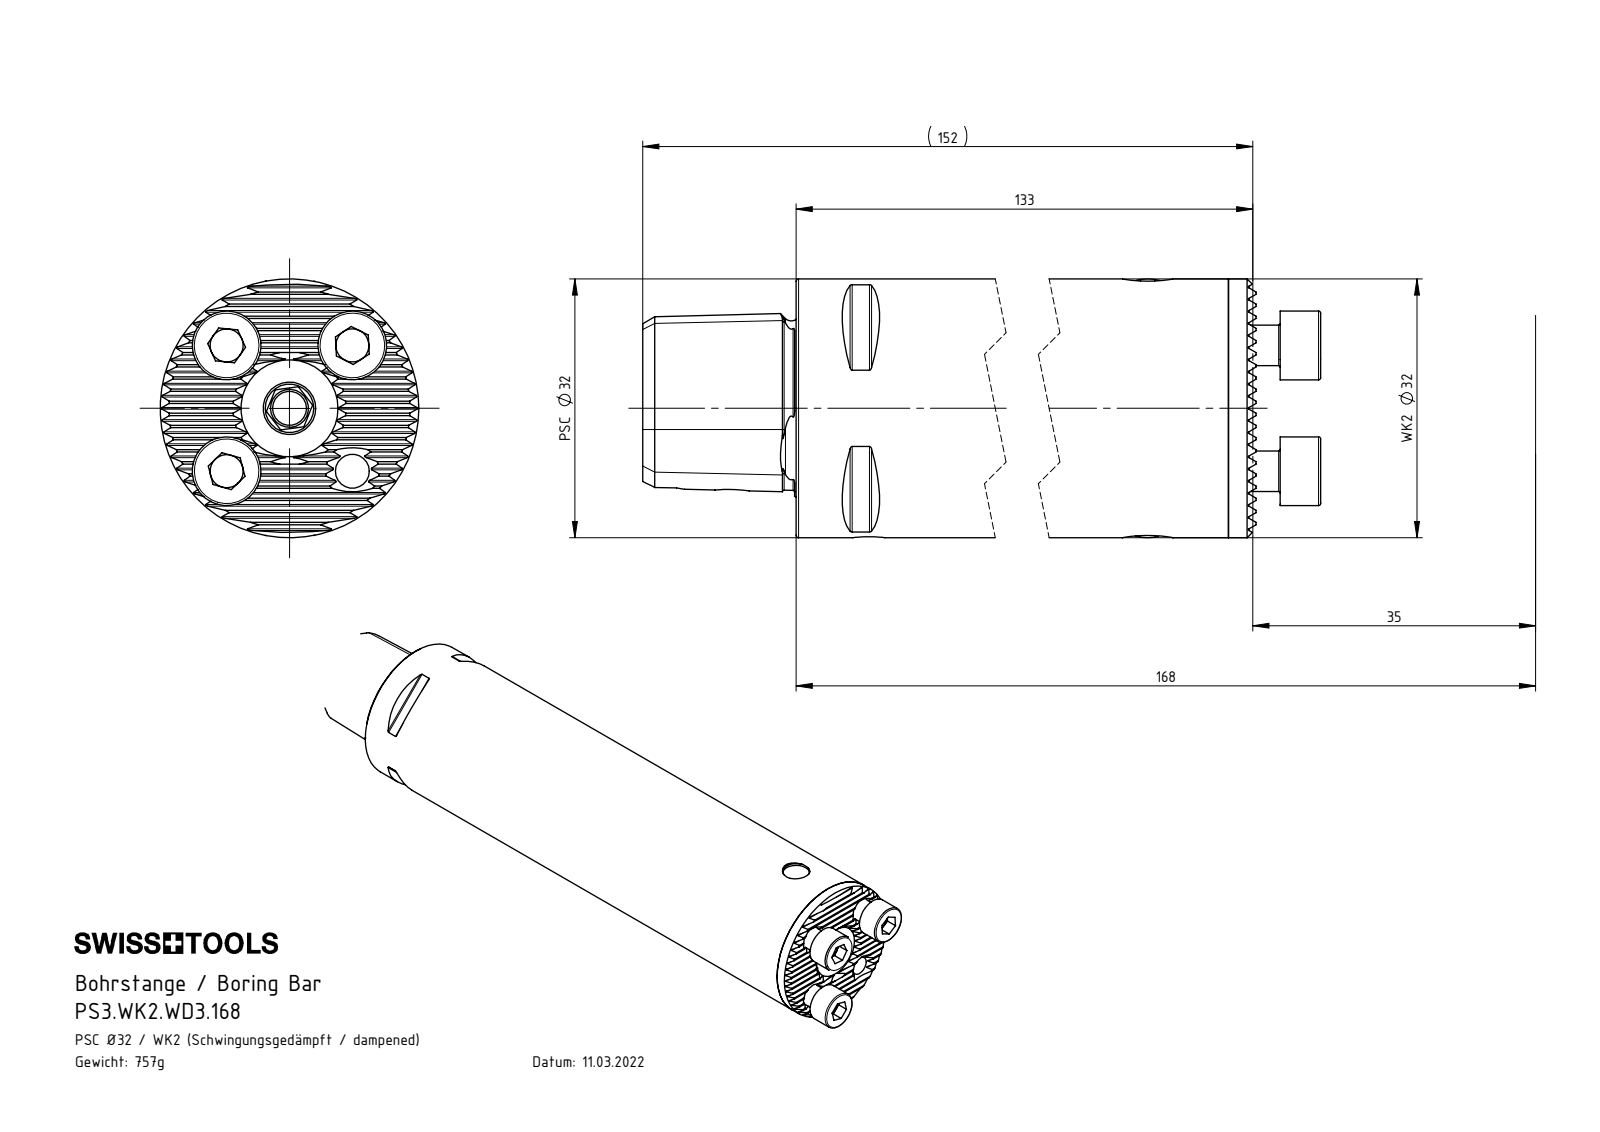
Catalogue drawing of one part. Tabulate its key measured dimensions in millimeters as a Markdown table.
| quantity | value |
| --- | --- |
| part name | DIN 3771 - 23x2; WD3-WK2.032.003_A; DIN 3771 - 6x1; WD3-ER1.027.019_A (+8 more) |
| STEP written by | SolidWorks 2017 (AUTOMOTIVE_DESIGN) |
| units | millimeters |
| bodies | 16 solids, 673 faces (236 planar, 163 cylindrical, 274 other) |
| overall size | 160.4 × 32 × 32 |
| volume | 100 978 mm³ |
| surface area | 56 780 mm² |
| round holes (diameter × count) | 4.2 × 5, 6 × 2, 3.6 × 1, 4 × 1, 6.8 × 1, 7 × 1, 7.4 × 1, 8.2 × 1, 8.5 × 1, 10.2 × 1, 12 × 1, 14 × 1 |
| round bosses / shafts (diameter × count) | 8.5 × 3, 5 × 3, 32 × 1, 27 × 1, 26.7 × 1, 26 × 1, 23.8 × 1, 13 × 1 |
| partial cylindrical surfaces (radius × count) | 0.12 × 21, 0.3 × 8, 3 × 1 |
| main face-to-face distances | 6, 93.4, 2.6, 1.3, 3.9, 3.2, 99.4, 100.25, 0.85, 6.75 |
| hole center spacings | 11, 15.56, 22.01, 17, 111, 128 |
